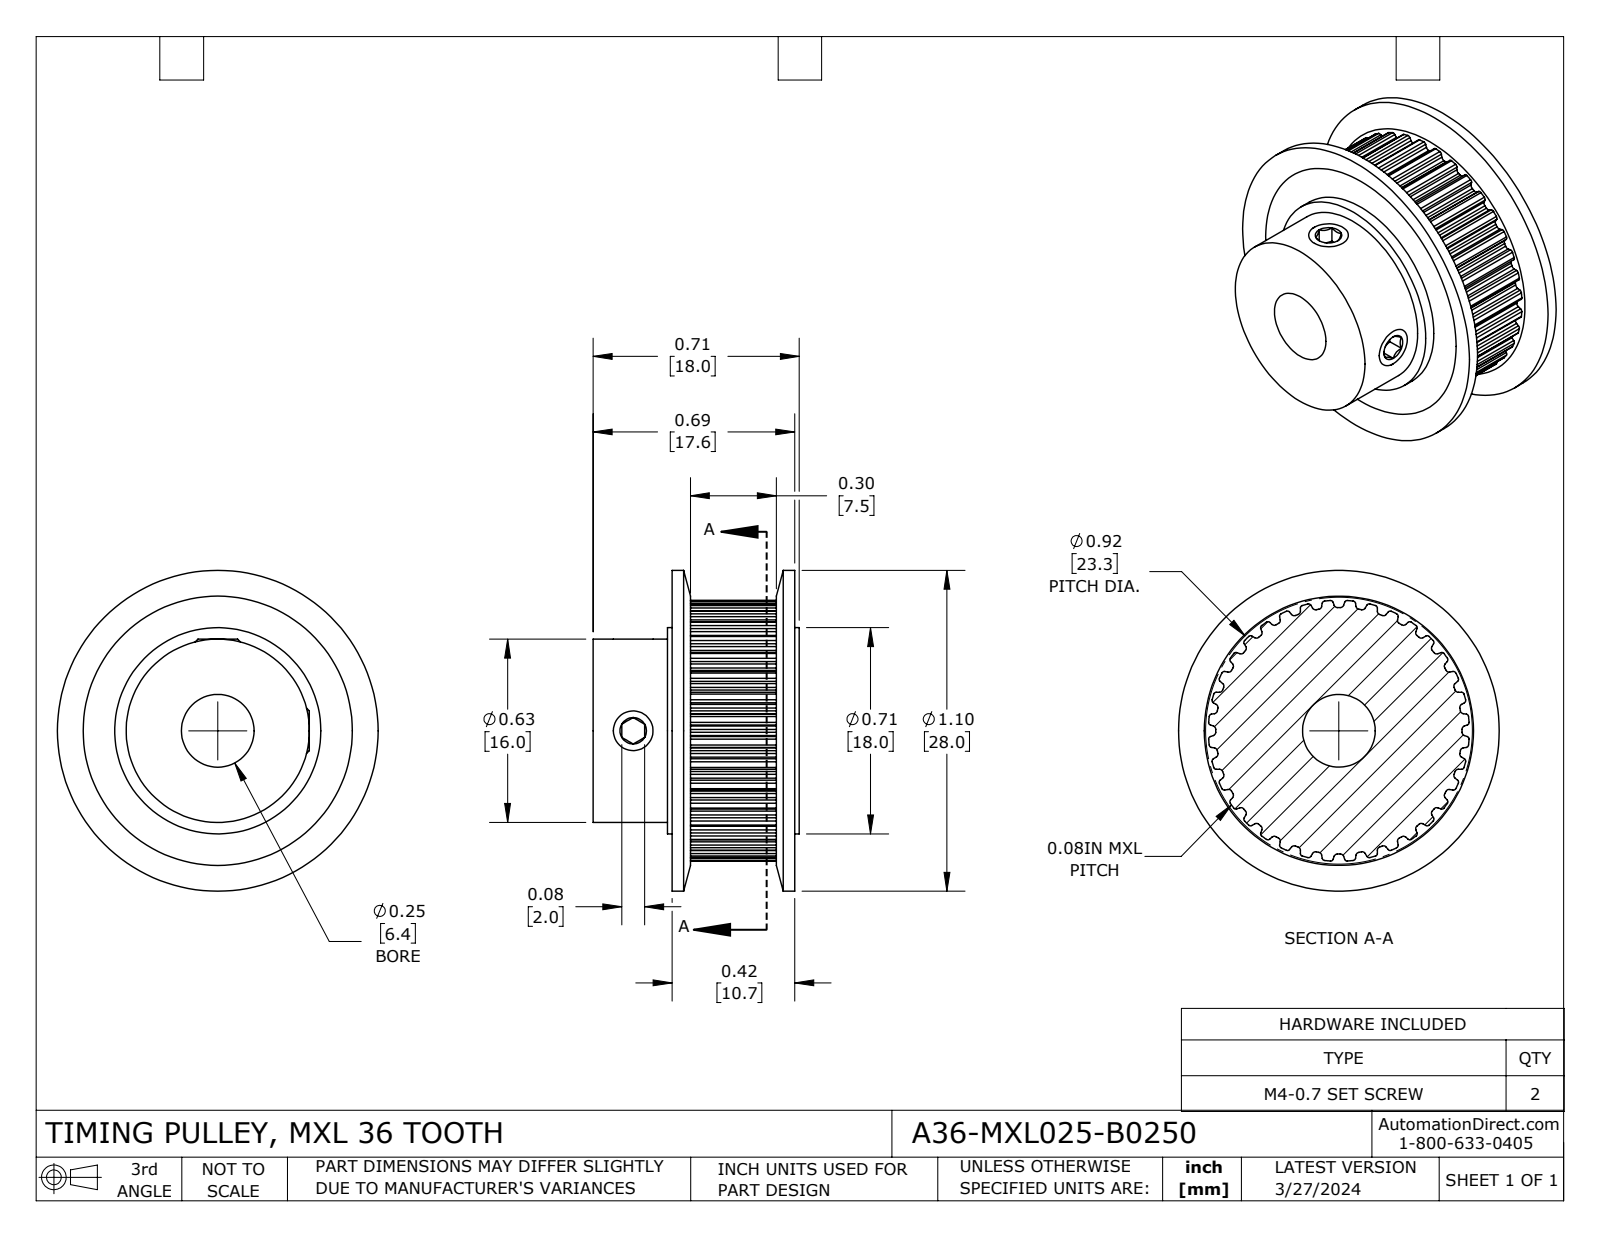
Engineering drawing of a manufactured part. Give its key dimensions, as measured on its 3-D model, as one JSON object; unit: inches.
{"part_name": "A36-MXL025-B0250", "step_written_by": "SolidWorks 2021 (CONFIG_CONTROL_DESIGN)", "units": "inches", "bodies": {"solids": 5, "faces": 400, "planar": 97, "cylindrical": 269, "other": 34}, "overall_size": [1.102, 1.102, 0.709], "volume_in3": 0.327, "surface_area_in2": 6.663, "round_holes": [[0.13, 2], [0.25, 1], [0.709, 1]], "round_bosses_or_shafts": [[0.157, 2], [1.102, 1], [0.63, 1]], "partial_cylinders_radius": [[0.009, 72], [0.012, 72], [0.423, 1], [0.448, 1]], "face_to_face_distances": [0.039, 0.335, 0.295, 0.374, 0.079, 0.413, 0.709, 0.669, 0.63, 0.265]}
